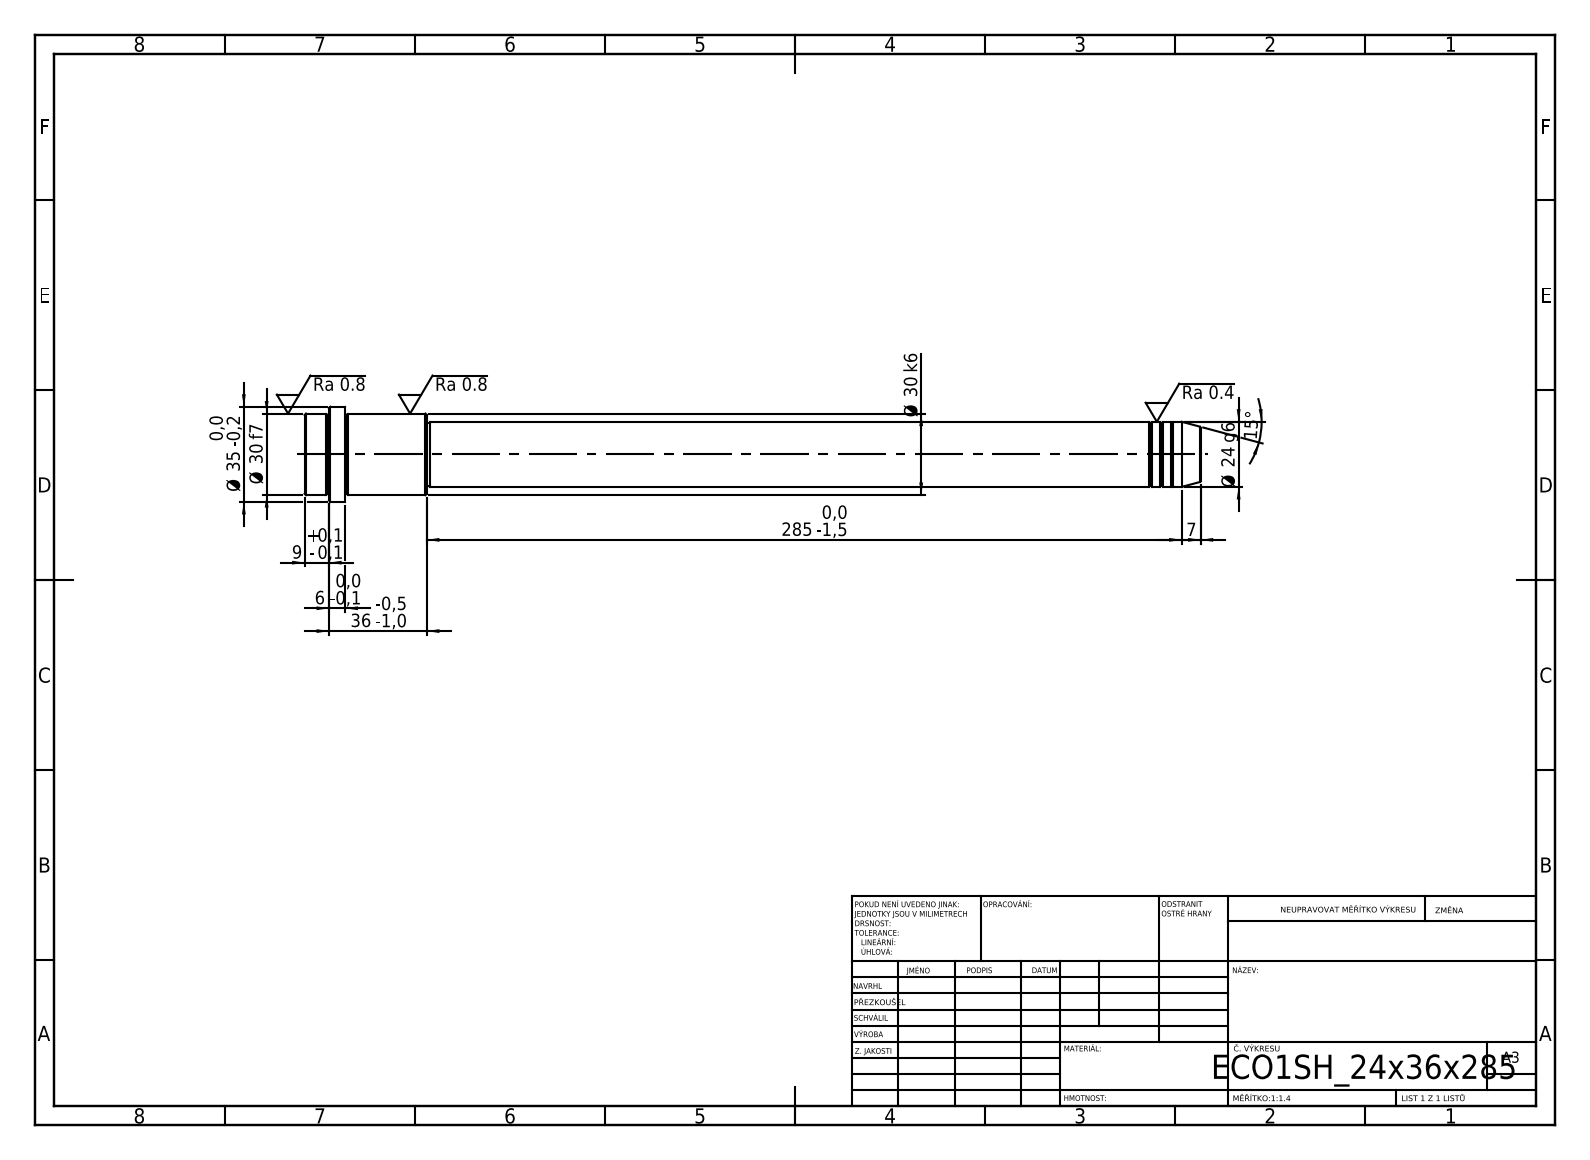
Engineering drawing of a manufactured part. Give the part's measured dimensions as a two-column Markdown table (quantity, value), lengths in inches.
| quantity | value |
| --- | --- |
| STEP written by | SolidWorks 2019 (CONFIG_CONTROL_DESIGN) |
| units | inches |
| bodies | 1 solid, 52 faces (6 planar, 16 cylindrical, 30 other) |
| overall size | 12.992 × 1.378 × 1.378 |
| volume | 9.859 in³ |
| surface area | 43.07 in² |
| round bosses / shafts (diameter × count) | 1.378 × 1, 1.181 × 1, 0.945 × 1, 0.906 × 1 |
| main face-to-face distances | 12.992, 12.402, 0.591, 11.22, 1.181, 1.772, 12.638, 1.417, 0.236, 0.354 |
